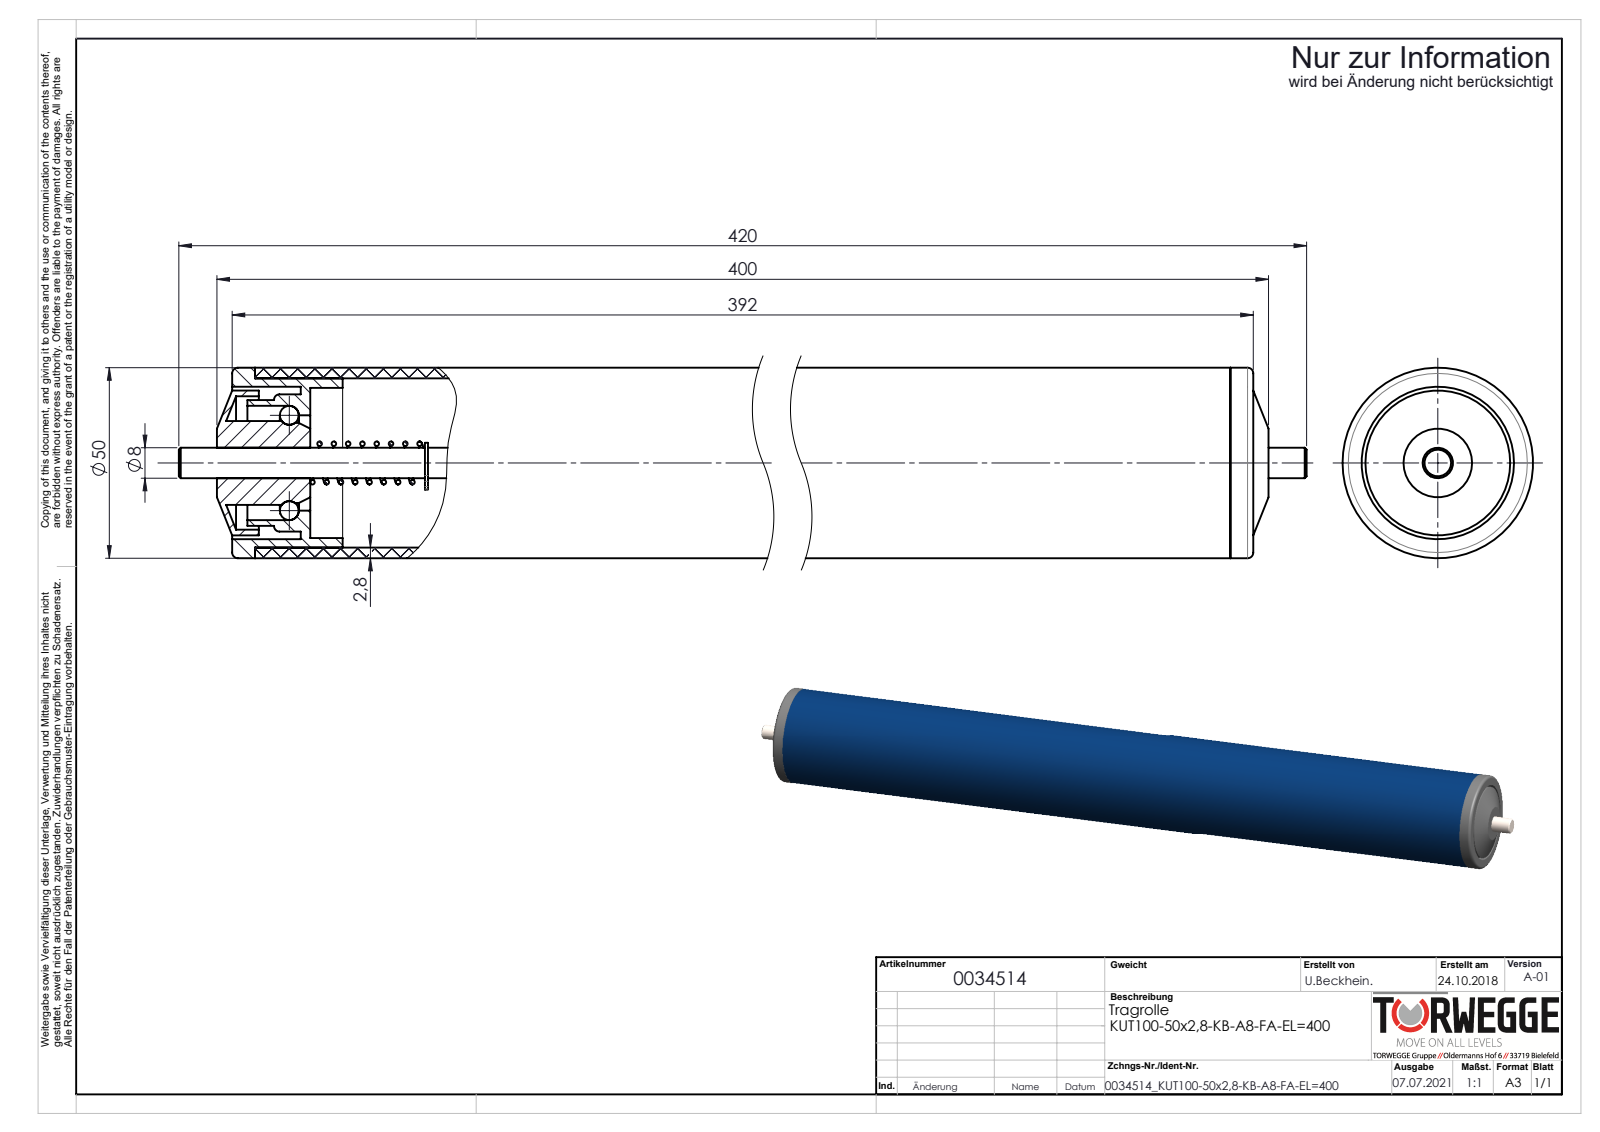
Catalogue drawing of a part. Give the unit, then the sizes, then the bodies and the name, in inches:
Units: inches
Overall size (bounding box): 16.535 × 1.969 × 1.969
Round holes (diameter × count): ⌀0.299 ×1, ⌀0.315 ×1, ⌀0.984 ×1, ⌀1.181 ×1, ⌀1.378 ×1, ⌀1.551 ×1, ⌀1.575 ×1
Round bosses / shafts (diameter × count): ⌀1.969 ×1, ⌀1.748 ×1, ⌀1.496 ×1, ⌀1.417 ×1, ⌀1.299 ×1, ⌀0.866 ×1, ⌀0.827 ×1
Partial cylindrical surfaces — rounded edges, fillets, slot ends (radius × count): R0.024 ×2, R0.03 ×2, R0.096 ×2, R0.192 ×1, R0.276 ×1
Main face-to-face distances: 0.571, 14.39, 0.433, 0.236, 0.807, 14.626, 15.197, 13.819, 14.961, 15.433
Volume: 14.33 in³ · Surface area: 256.9 in²
Bodies: 11 solids, 186 faces (52 planar, 88 cylindrical, 46 other)
Part name (STEP PRODUCT): 0034514
STEP written by: SolidWorks 2020 (AUTOMOTIVE_DESIGN)
